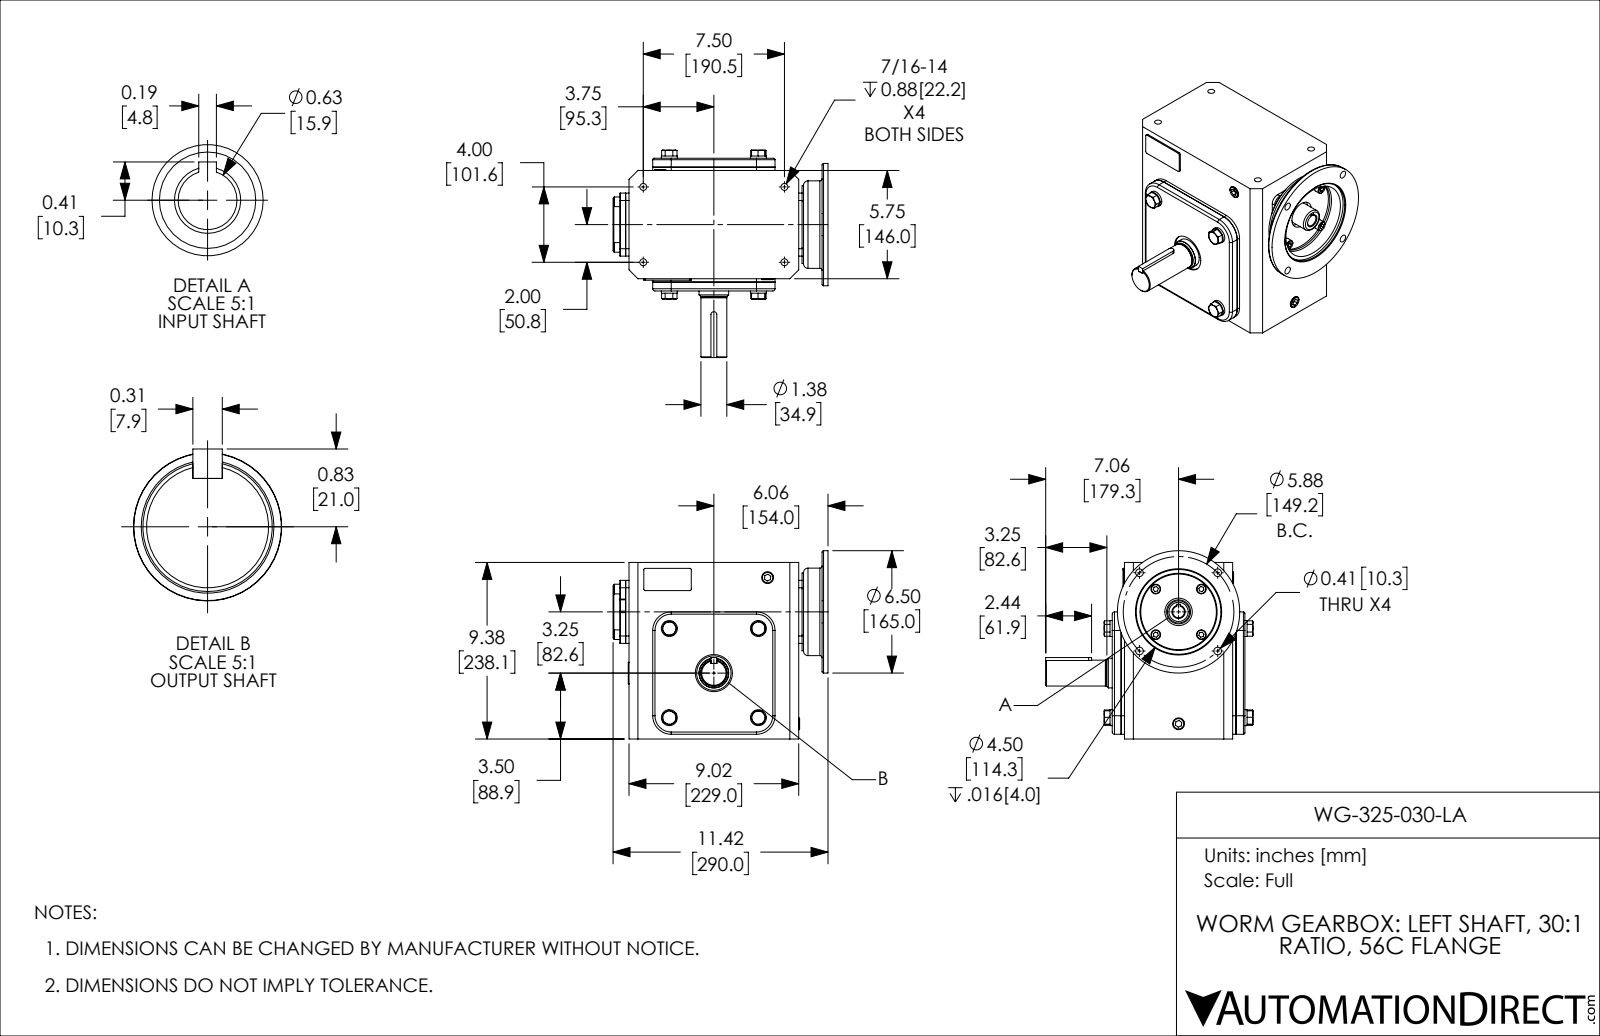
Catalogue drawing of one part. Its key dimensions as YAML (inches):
part_name: "WG-325-030-LA"
step_written_by: "SolidWorks 2017 (AUTOMOTIVE_DESIGN)"
units: inches
bodies: {solids: 39, faces: 575, planar: 318, cylindrical: 167, other: 90}
overall_size: [11.417, 11.014, 9.998]
volume: 503.5
surface_area: 897.2
round_holes:
  - {diameter: 0.368, count: 4}
  - {diameter: 0.406, count: 4}
  - {diameter: 0.628, count: 3}
  - {diameter: 0.591, count: 1}
  - {diameter: 0.625, count: 1}
  - {diameter: 0.978, count: 1}
  - {diameter: 1.181, count: 1}
  - {diameter: 1.457, count: 1}
  - {diameter: 1.969, count: 1}
  - {diameter: 2.441, count: 1}
  - {diameter: 2.756, count: 1}
  - {diameter: 4.016, count: 1}
round_bosses_or_shafts:
  - {diameter: 0.846, count: 4}
  - {diameter: 0.512, count: 4}
  - {diameter: 6.496, count: 1}
  - {diameter: 4.646, count: 1}
  - {diameter: 4.134, count: 1}
  - {diameter: 2.835, count: 1}
  - {diameter: 1.575, count: 1}
  - {diameter: 1.375, count: 1}
partial_cylinders:
  - {radius: 0.079, count: 11}
  - {radius: 0.118, count: 4}
  - {radius: 0.394, count: 4}
  - {radius: 0.906, count: 4}
  - {radius: 0.984, count: 4}
  - {radius: 0.02, count: 2}
  - {radius: 0.039, count: 2}
  - {radius: 0.156, count: 1}
face_to_face_distances: [0.079, 0.177, 6.496, 0.394, 6.969, 0.472, 6.575, 6.398, 0.571, 0.65]
hole_center_spacings: [2.937, 4.154, 2.385, 4, 4.389, 5.718, 5.817, 5.875]
